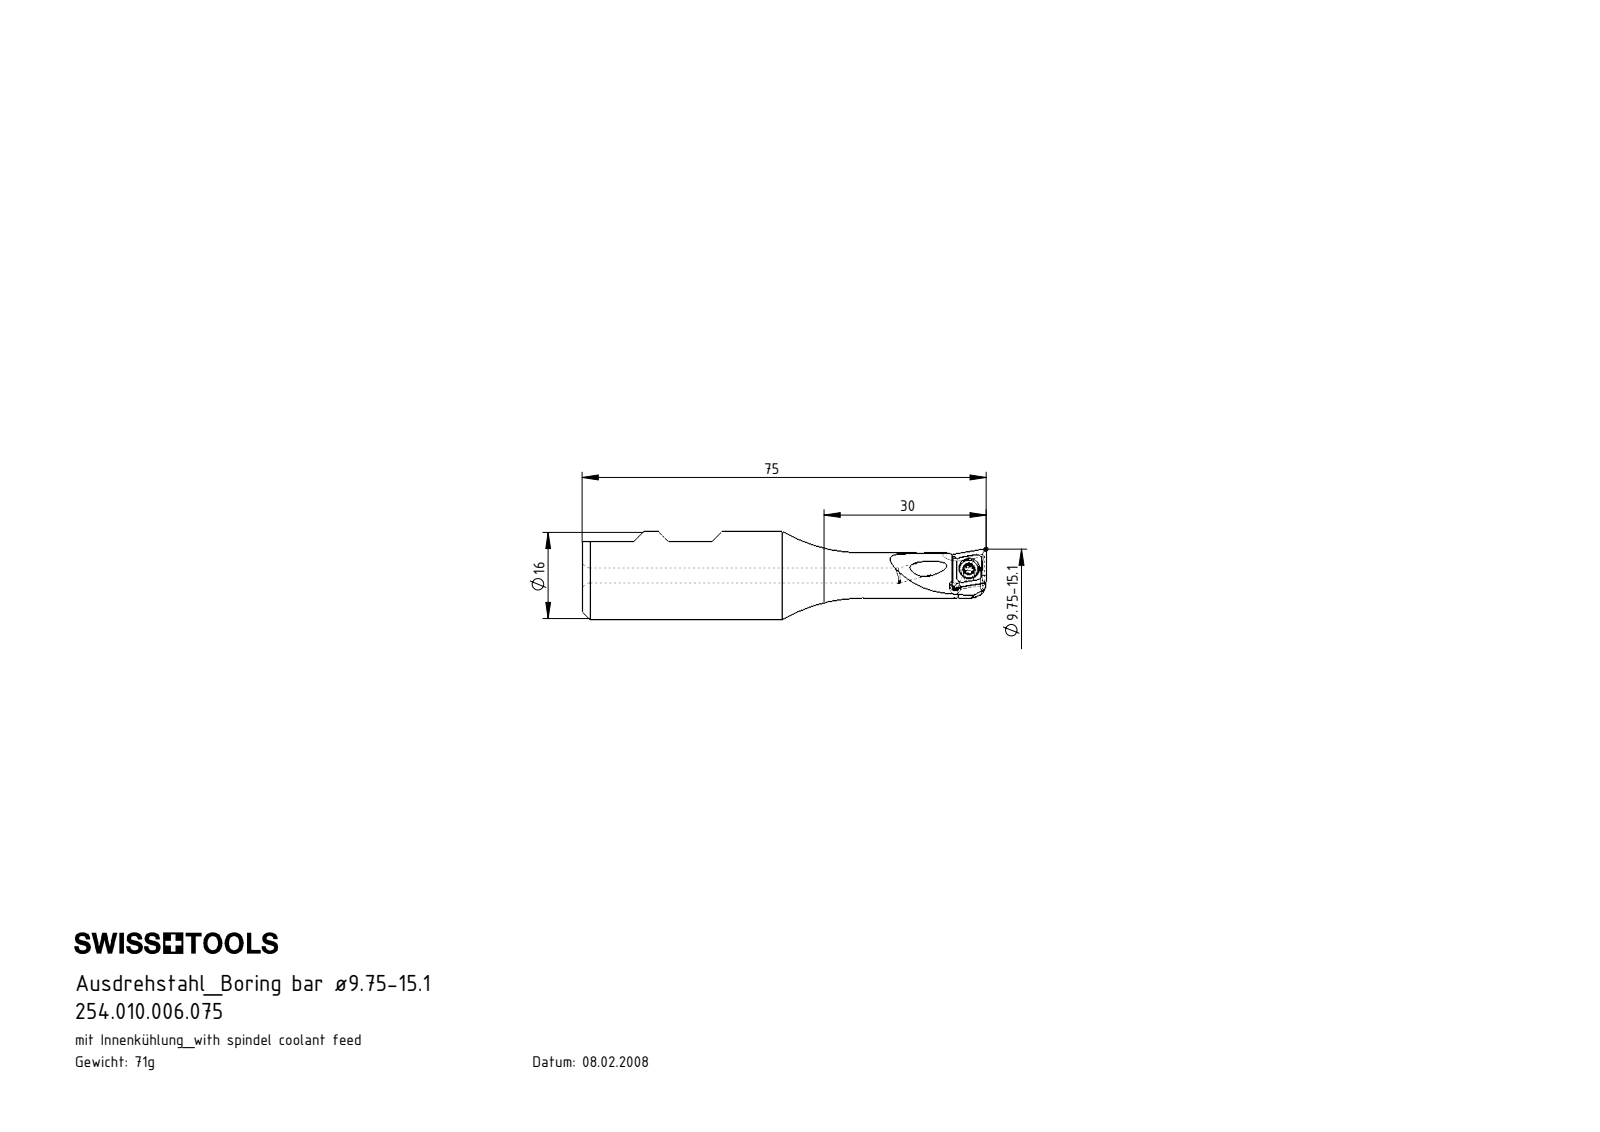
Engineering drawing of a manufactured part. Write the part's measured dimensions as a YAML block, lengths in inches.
part_name: "WCA-ER2.001.005_A; 254.010.006.075; CCMT060204; B10-WCA.K11.075_C_mit beschriftung"
step_written_by: "SolidWorks 2017 (CONFIG_CONTROL_DESIGN)"
units: inches
bodies: {solids: 3, faces: 163, planar: 34, cylindrical: 70, other: 59}
overall_size: [2.953, 0.63, 0.63]
volume: 0.551
surface_area: 6.068
round_holes:
  - {diameter: 0.118, count: 2}
  - {diameter: 0.081, count: 1}
  - {diameter: 0.083, count: 1}
  - {diameter: 0.11, count: 1}
  - {diameter: 0.152, count: 1}
round_bosses_or_shafts:
  - {diameter: 0.63, count: 1}
  - {diameter: 0.317, count: 1}
  - {diameter: 0.134, count: 1}
  - {diameter: 0.098, count: 1}
partial_cylinders:
  - {radius: 0.008, count: 6}
  - {radius: 0.014, count: 5}
  - {radius: 0.014, count: 1}
  - {radius: 0.039, count: 1}
  - {radius: 0.138, count: 1}
  - {radius: 0.161, count: 1}
  - {radius: 0.197, count: 1}
  - {radius: 0.276, count: 1}
face_to_face_distances: [0.09, 0.404, 0.094, 2.709, 0.058, 0.031, 0.035, 0.103, 0.161, 0.193]
hole_center_spacings: [0.157, 0.161]
